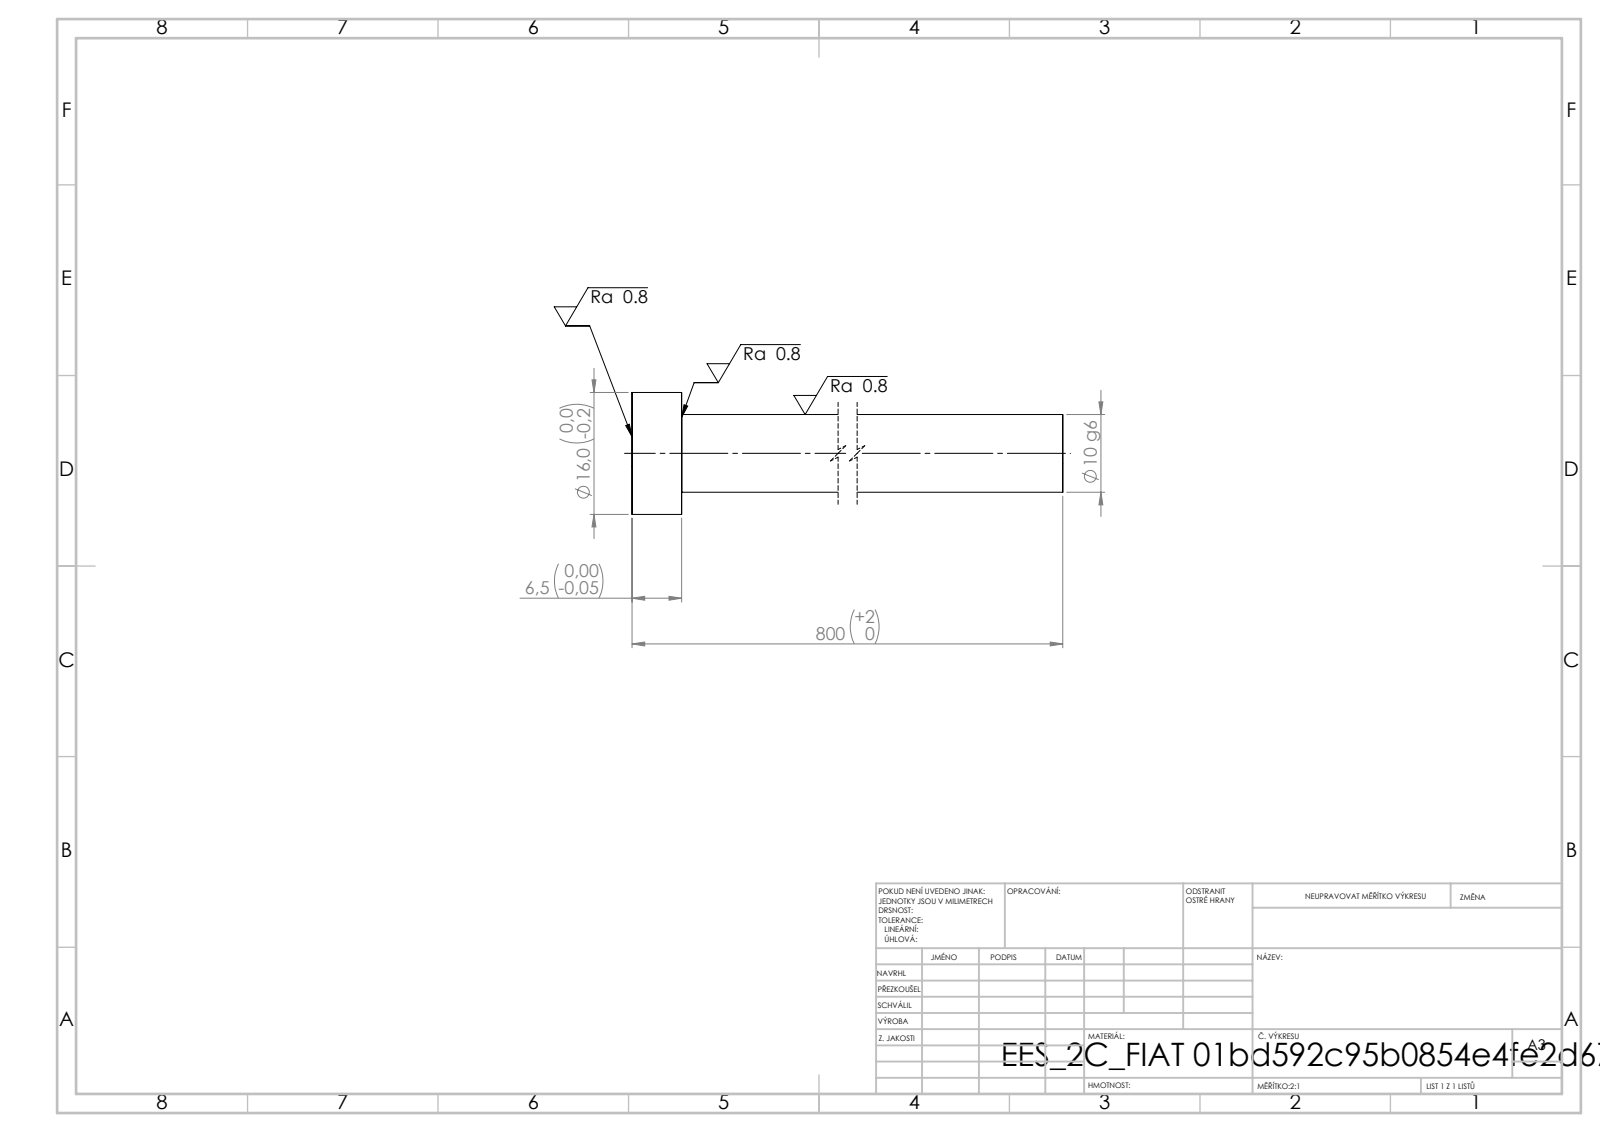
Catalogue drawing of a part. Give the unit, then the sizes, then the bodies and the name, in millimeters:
Units: millimetres
Overall size (bounding box): 800 × 16 × 16
Round bosses / shafts (diameter × count): ⌀16 ×1, ⌀10.2 ×1
Main face-to-face distances: 6.5, 800, 793.5
Volume: 66 146 mm³ · Surface area: 26 156 mm²
Bodies: 1 solid, 7 faces (3 planar, 4 cylindrical, 0 other)
STEP written by: SolidWorks 2019 (CONFIG_CONTROL_DESIGN)
